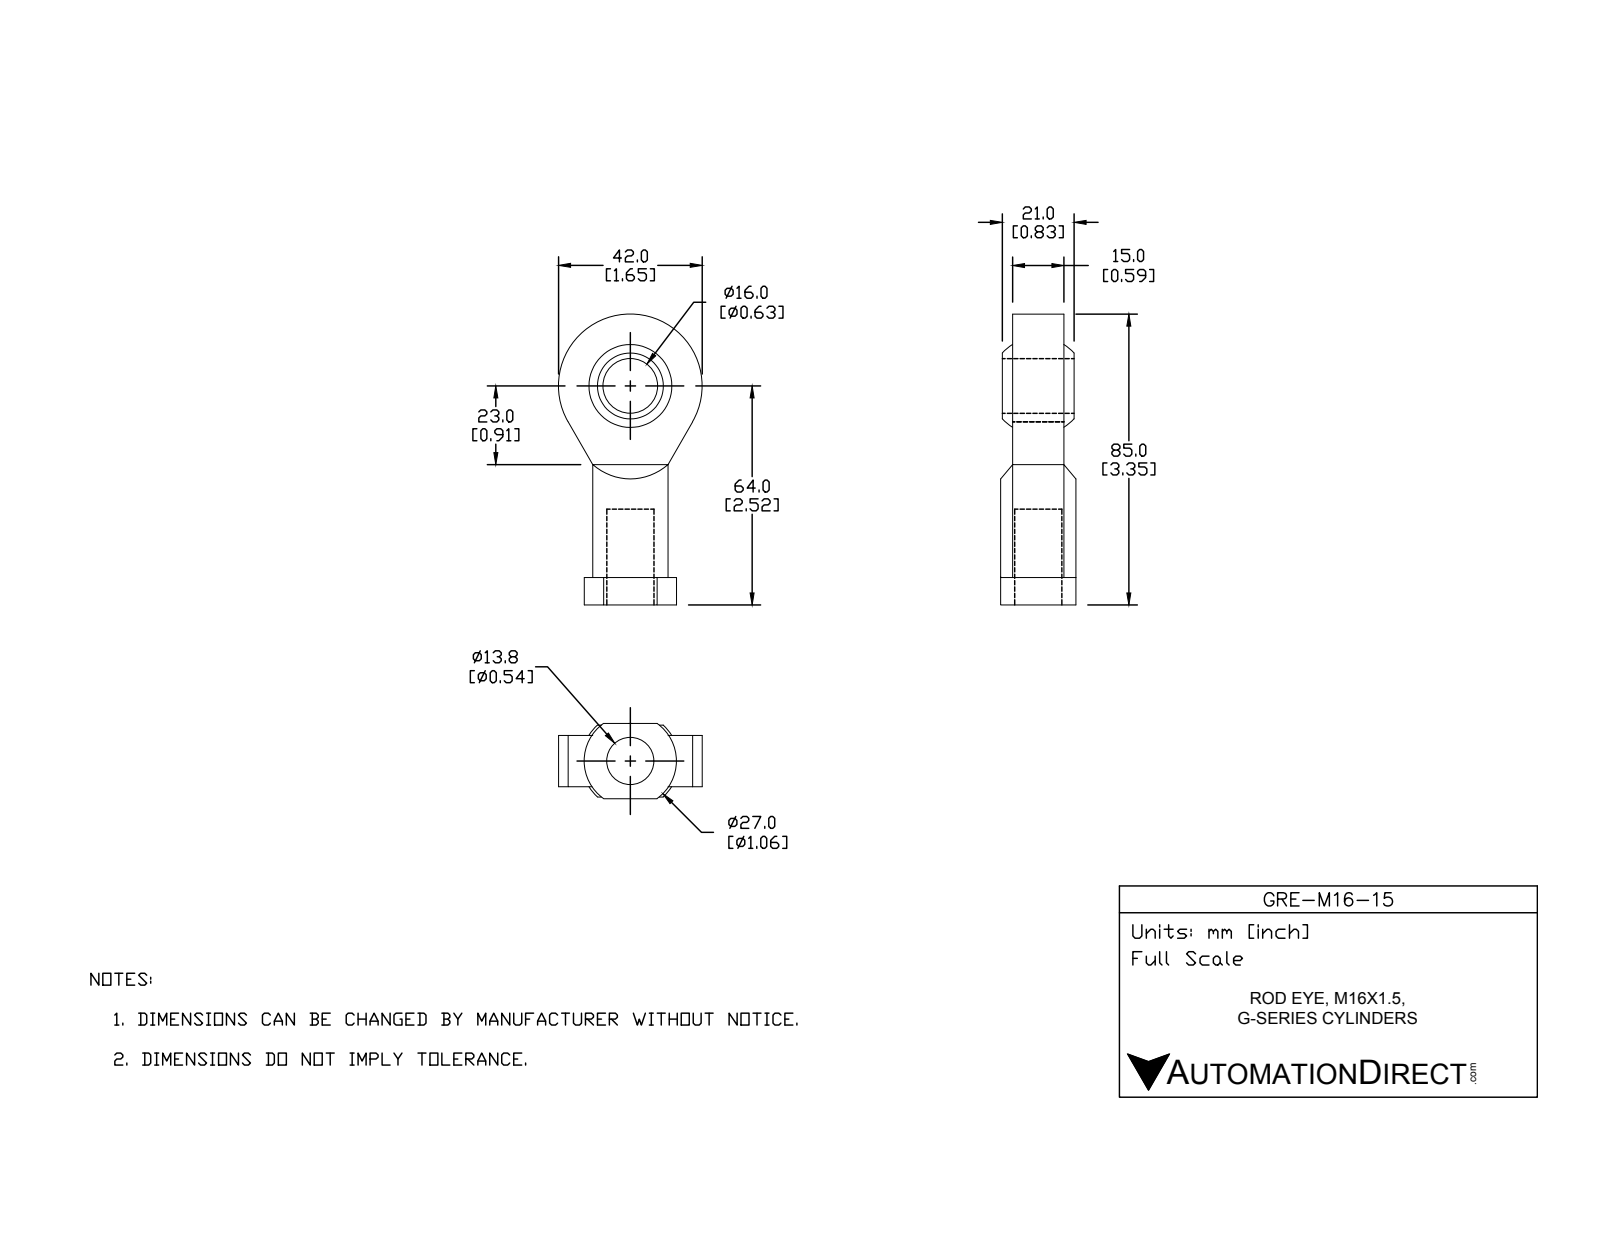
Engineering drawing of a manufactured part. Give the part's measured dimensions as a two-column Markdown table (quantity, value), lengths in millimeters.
| quantity | value |
| --- | --- |
| part name | GRE-M16-15 |
| STEP written by | SolidWorks 2017 (AUTOMOTIVE_DESIGN) |
| units | millimeters |
| bodies | 1 solid, 34 faces (9 planar, 9 cylindrical, 16 other) |
| overall size | 85.7 × 42 × 21.7 |
| volume | 28 211 mm³ |
| surface area | 11 156 mm² |
| round holes (diameter × count) | 14.65 × 1, 15.85 × 1 |
| round bosses / shafts (diameter × count) | 21.6 × 1 |
| partial cylindrical surfaces (radius × count) | 13.5 × 1, 21 × 1 |
| main face-to-face distances | 14.8, 3.45, 18.25, 21.7, 0.35, 21.35, 3.1, 17.9, 21 |
